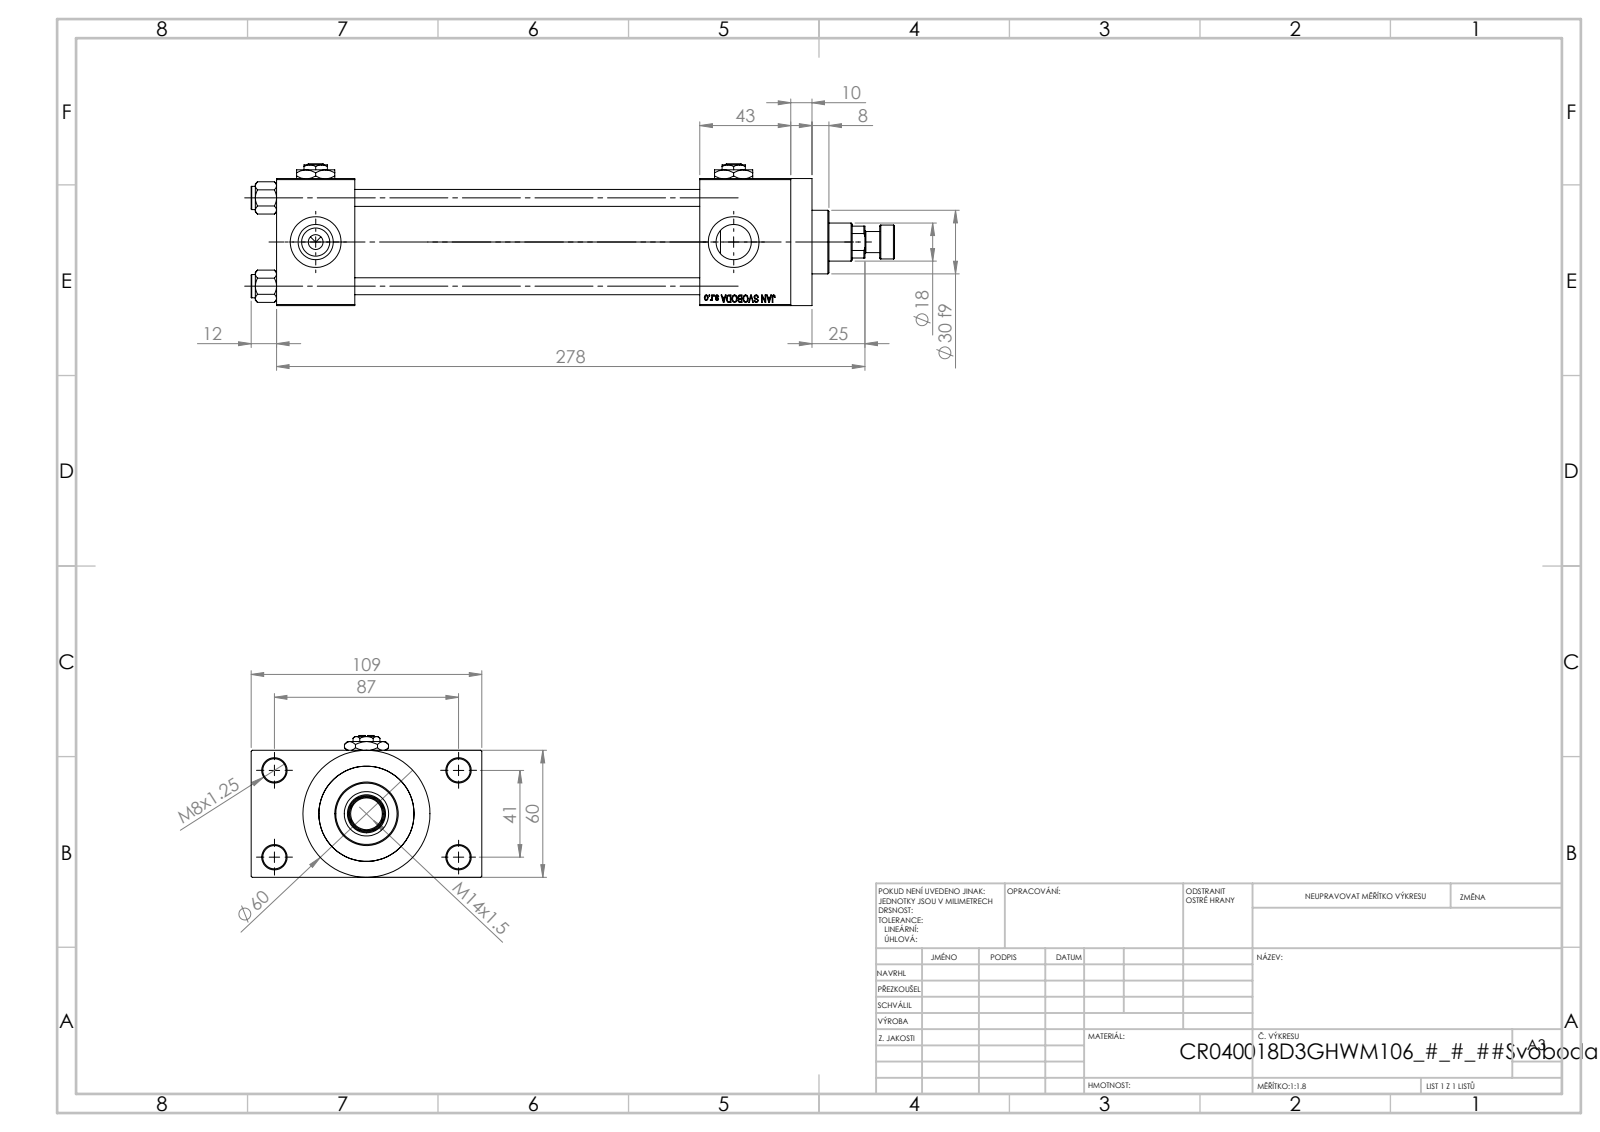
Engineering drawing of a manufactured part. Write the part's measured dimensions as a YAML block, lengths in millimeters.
part_name: "V215CR_D_Body; Zatka_pro_OIL_PORT; V215CR_D_TYCINKA; NUT_M5_D (+3 more)"
step_written_by: "SolidWorks 2019 (CONFIG_CONTROL_DESIGN)"
units: millimeters
bodies: {solids: 14, faces: 1218, planar: 549, cylindrical: 103, other: 566}
overall_size: [304, 109, 67]
volume: 602677
surface_area: 171030
round_holes:
  - {diameter: 8, count: 4}
  - {diameter: 11, count: 4}
  - {diameter: 16.66, count: 4}
  - {diameter: 24, count: 4}
  - {diameter: 7, count: 3}
  - {diameter: 8.5, count: 1}
  - {diameter: 18, count: 1}
  - {diameter: 21, count: 1}
  - {diameter: 31, count: 1}
  - {diameter: 40, count: 1}
  - {diameter: 45, count: 1}
round_bosses_or_shafts:
  - {diameter: 11, count: 4}
  - {diameter: 60, count: 1}
  - {diameter: 46, count: 1}
  - {diameter: 30, count: 1}
  - {diameter: 16, count: 1}
  - {diameter: 10, count: 1}
partial_cylinders:
  - {radius: 8.5, count: 1}
face_to_face_distances: [60, 24.5, 163, 84.5, 37, 200, 43, 243, 206, 10]
hole_center_spacings: [22.65, 29.49, 41.7, 47.15, 48.09, 64.35, 76.49, 41]
